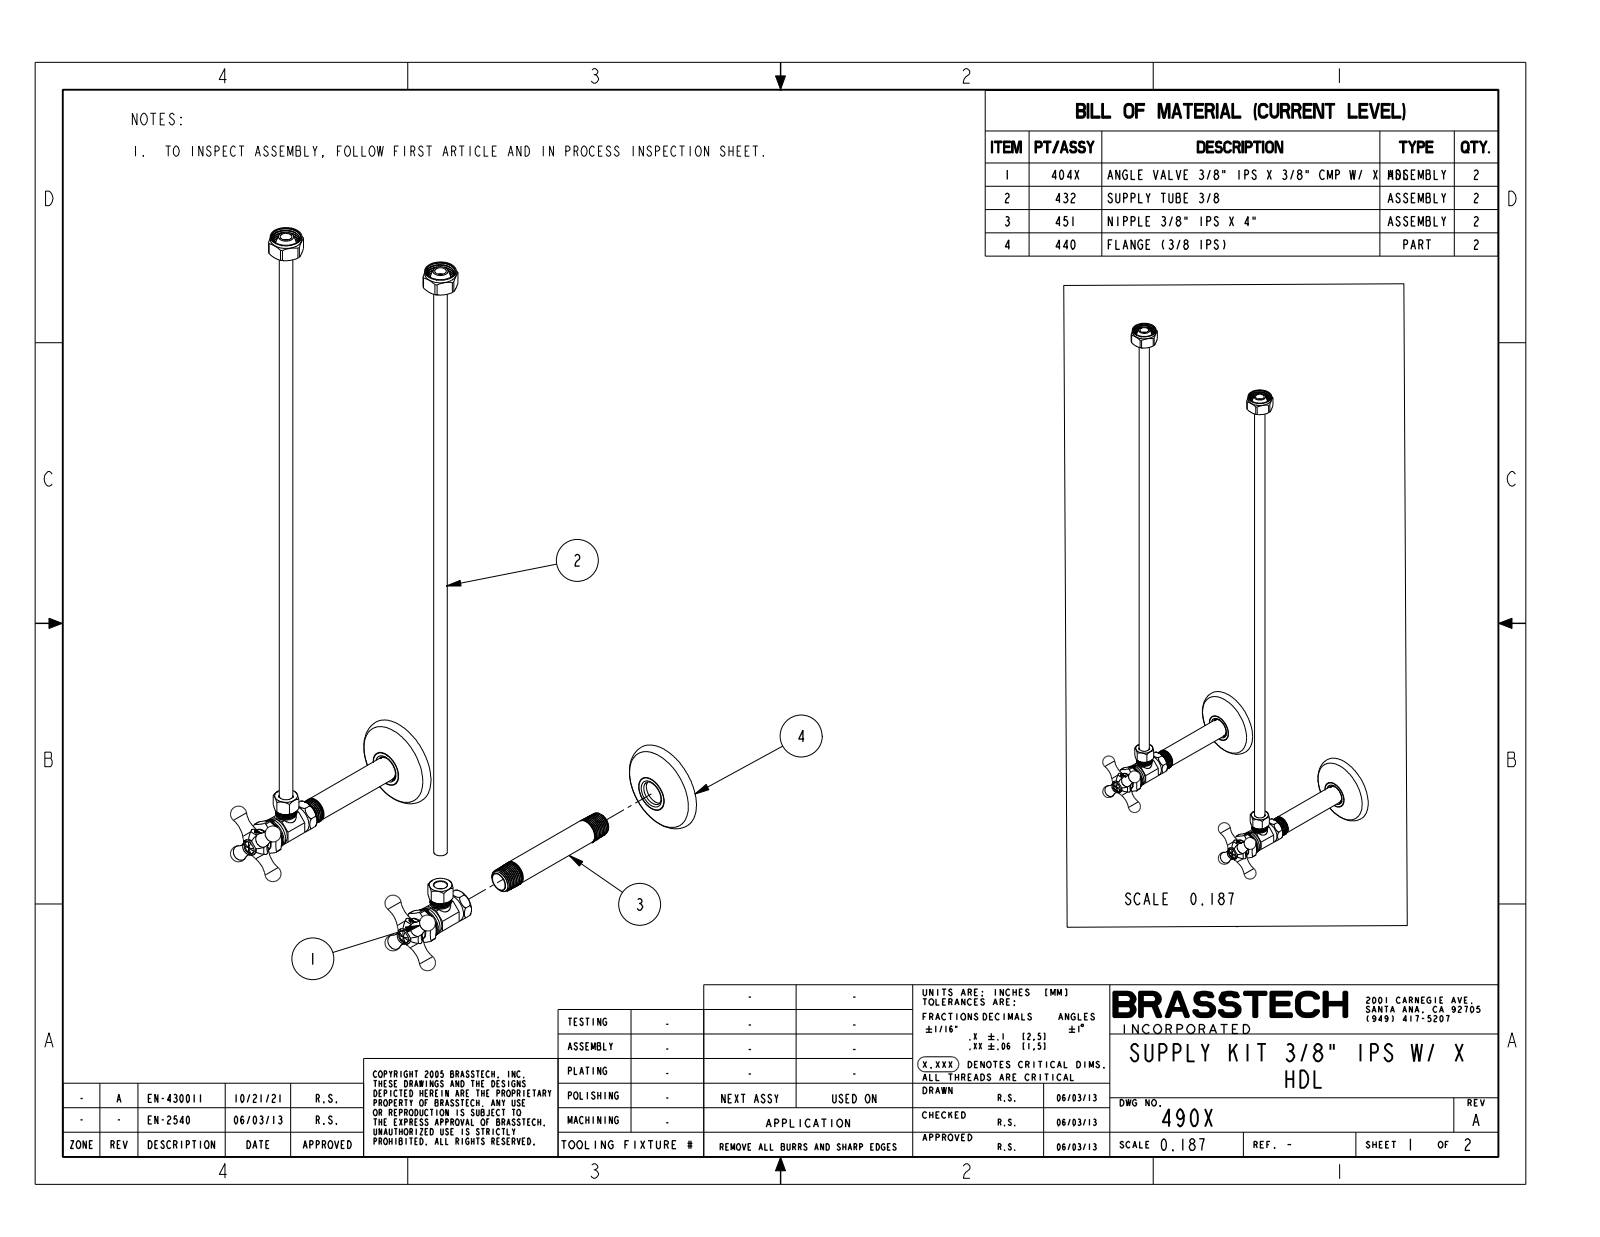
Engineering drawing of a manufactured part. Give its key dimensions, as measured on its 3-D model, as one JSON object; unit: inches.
{"part_name": "490X", "step_written_by": "CREO PARAMETRIC BY PTC INC, 2018500 (CONFIG_CONTROL_DESIGN)", "units": "inches", "bodies": {"solids": 10, "faces": 1596, "planar": 372, "cylindrical": 580, "other": 644}, "overall_size": [21.11, 8.5, 5.971], "volume_in3": 3.488, "surface_area_in2": 261, "round_holes": [[0.13, 2], [0.32, 2], [0.375, 2], [0.377, 2], [0.392, 2], [0.4, 2], [0.464, 2], [0.48, 2], [0.515, 2], [0.52, 2], [0.563, 2], [0.623, 2]], "round_bosses_or_shafts": [[0.655, 4], [0.867, 2], [0.86, 2], [0.753, 2], [0.725, 2], [0.68, 2], [0.677, 2], [0.675, 2]], "partial_cylinders_radius": [[0.01, 36], [0.05, 12], [0.17, 2], [0.256, 2], [0.376, 2], [0.489, 2], [0.188, 1]], "face_to_face_distances": [0.8, 3, 0.625, 5.196, 6, 0.875, 0.875, 0.087, 0.713, 4.242], "hole_center_spacings": [6, 1.11, 6.102]}
